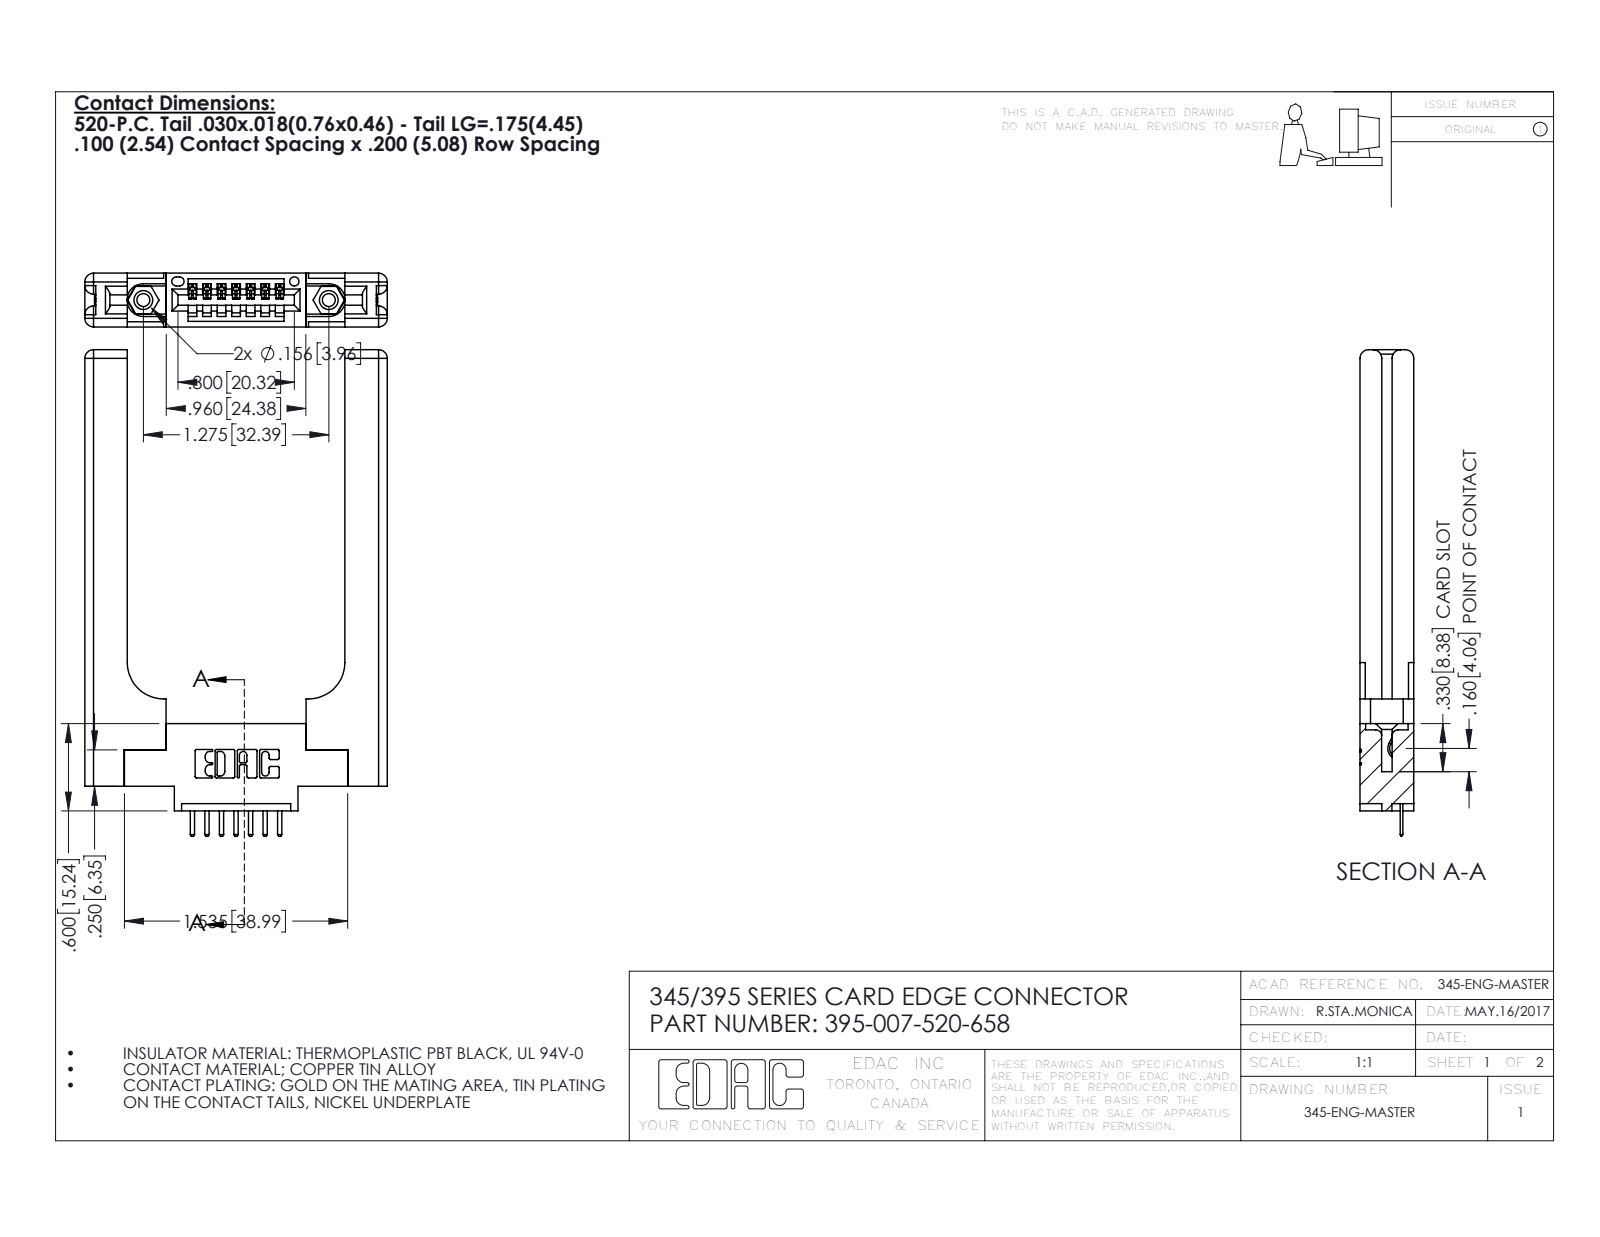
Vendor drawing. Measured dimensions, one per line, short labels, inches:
name: 345-292-001_345-293-120; 395-007-520-658; 345-250-001_345-250-001-102; 345-220-058_345-220-058 (+1 more)
written by: SolidWorks 2016 (CONFIG_CONTROL_DESIGN)
unit: in
bodies: 12 solids, 820 faces (526 planar, 234 cylindrical, 60 other)
size: 3.345 × 2.079 × 0.37
volume: 0.799 in³; area: 17.05 in²
holes: 2× ⌀0.089, 2× ⌀0.125, 2× ⌀0.156, 1× ⌀0.064
bosses: 2× ⌀0.155
rounds: 22× R0.01, 16× R0.01, 16× R0.06, 14× R0.006, 6× R0.007, 6× R0.031, 3× R0.026, 2× R0.03
face distances: 0.37, 0.15, 0.22, 0.072, 0.148, 0.077, 1.496, 0.298, 0.071, 0.12
hole spacings: 0.27, 1.045, 1.275
